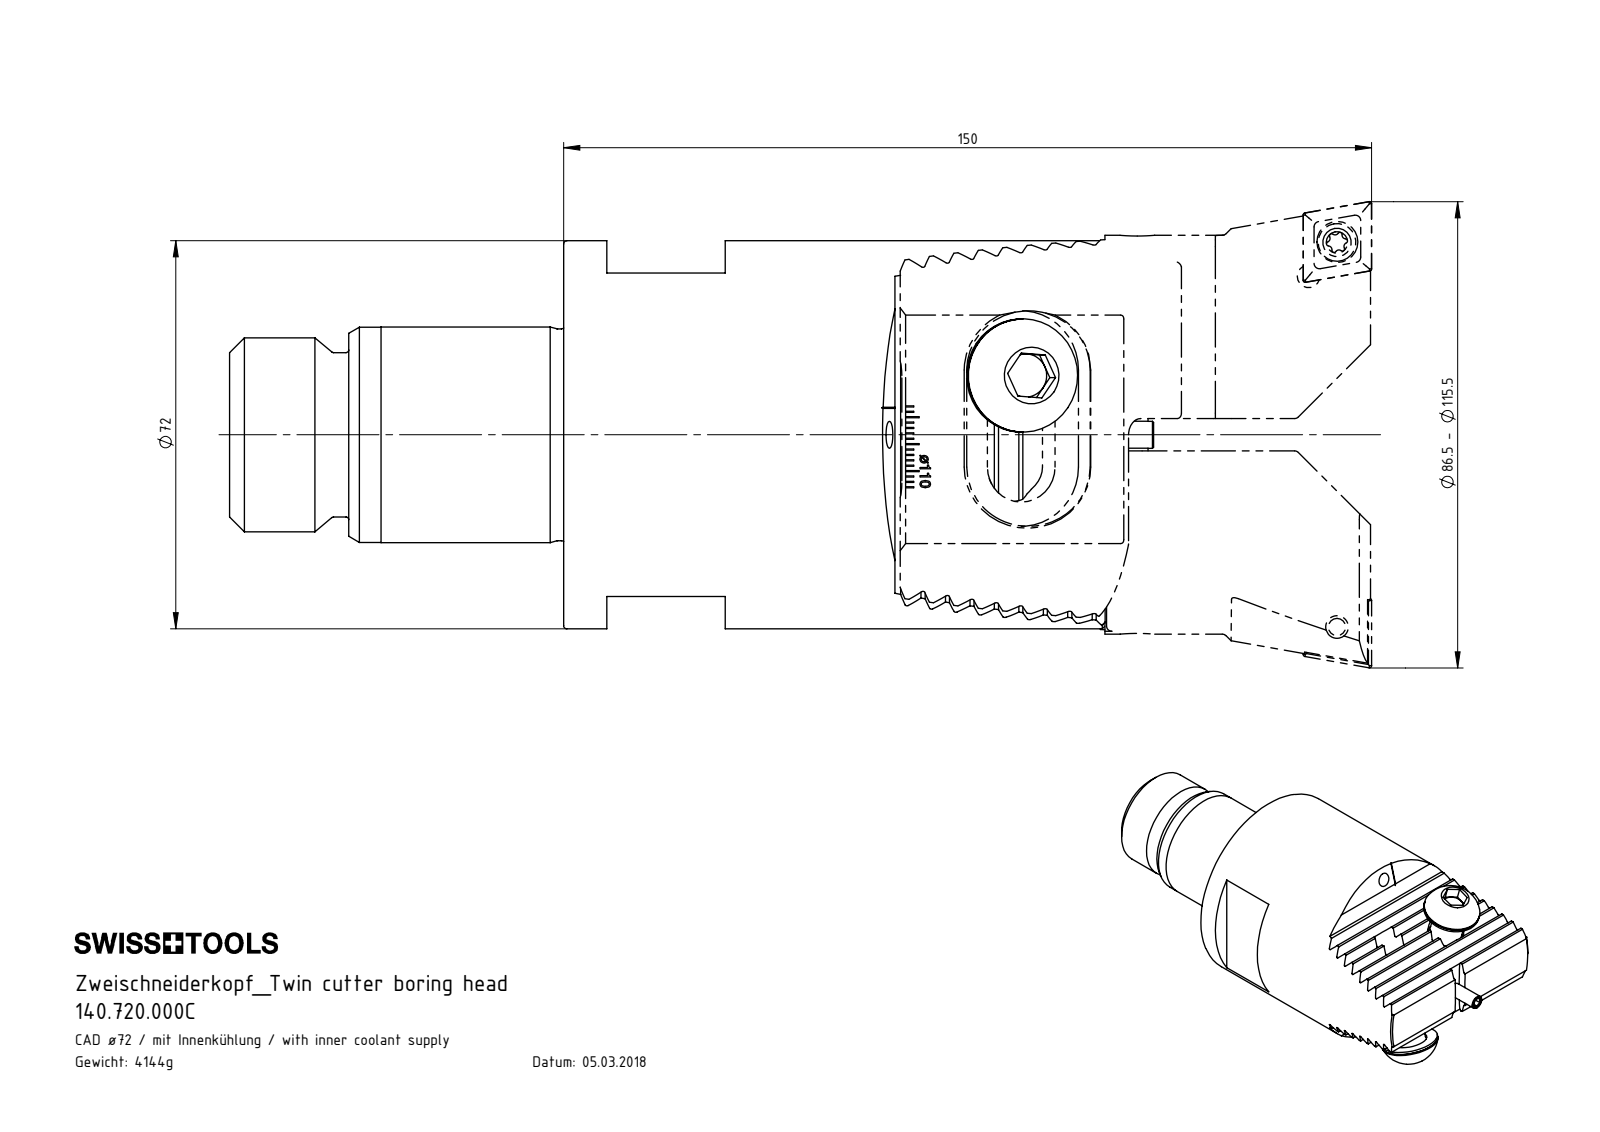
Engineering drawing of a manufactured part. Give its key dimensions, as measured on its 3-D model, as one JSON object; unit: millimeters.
{"part_name": "140.720.000C; Z72-ER1.001.025; Z42-ER2.001.019_A; Z72-ER1.002.025_A (+2 more)", "step_written_by": "SolidWorks 2017 (CONFIG_CONTROL_DESIGN)", "units": "millimeters", "bodies": {"solids": 6, "faces": 328, "planar": 159, "cylindrical": 97, "other": 72}, "overall_size": [171.5, 72, 72], "volume_mm3": 385286, "surface_area_mm2": 50732, "round_holes": [[5, 3], [10.25, 2], [13, 2], [13.5, 2], [3, 1], [3.3, 1], [8.5, 1]], "round_bosses_or_shafts": [[21, 2], [12, 2], [72, 1], [40, 1], [39.95, 1], [39.3, 1], [36, 1], [30.5, 1]], "partial_cylinders_radius": [[0.34, 18], [220, 2]], "face_to_face_distances": [4.07, 8.14, 12.21, 20.36, 16.28, 16.29, 24.43, 12.22, 100.5, 60]}
